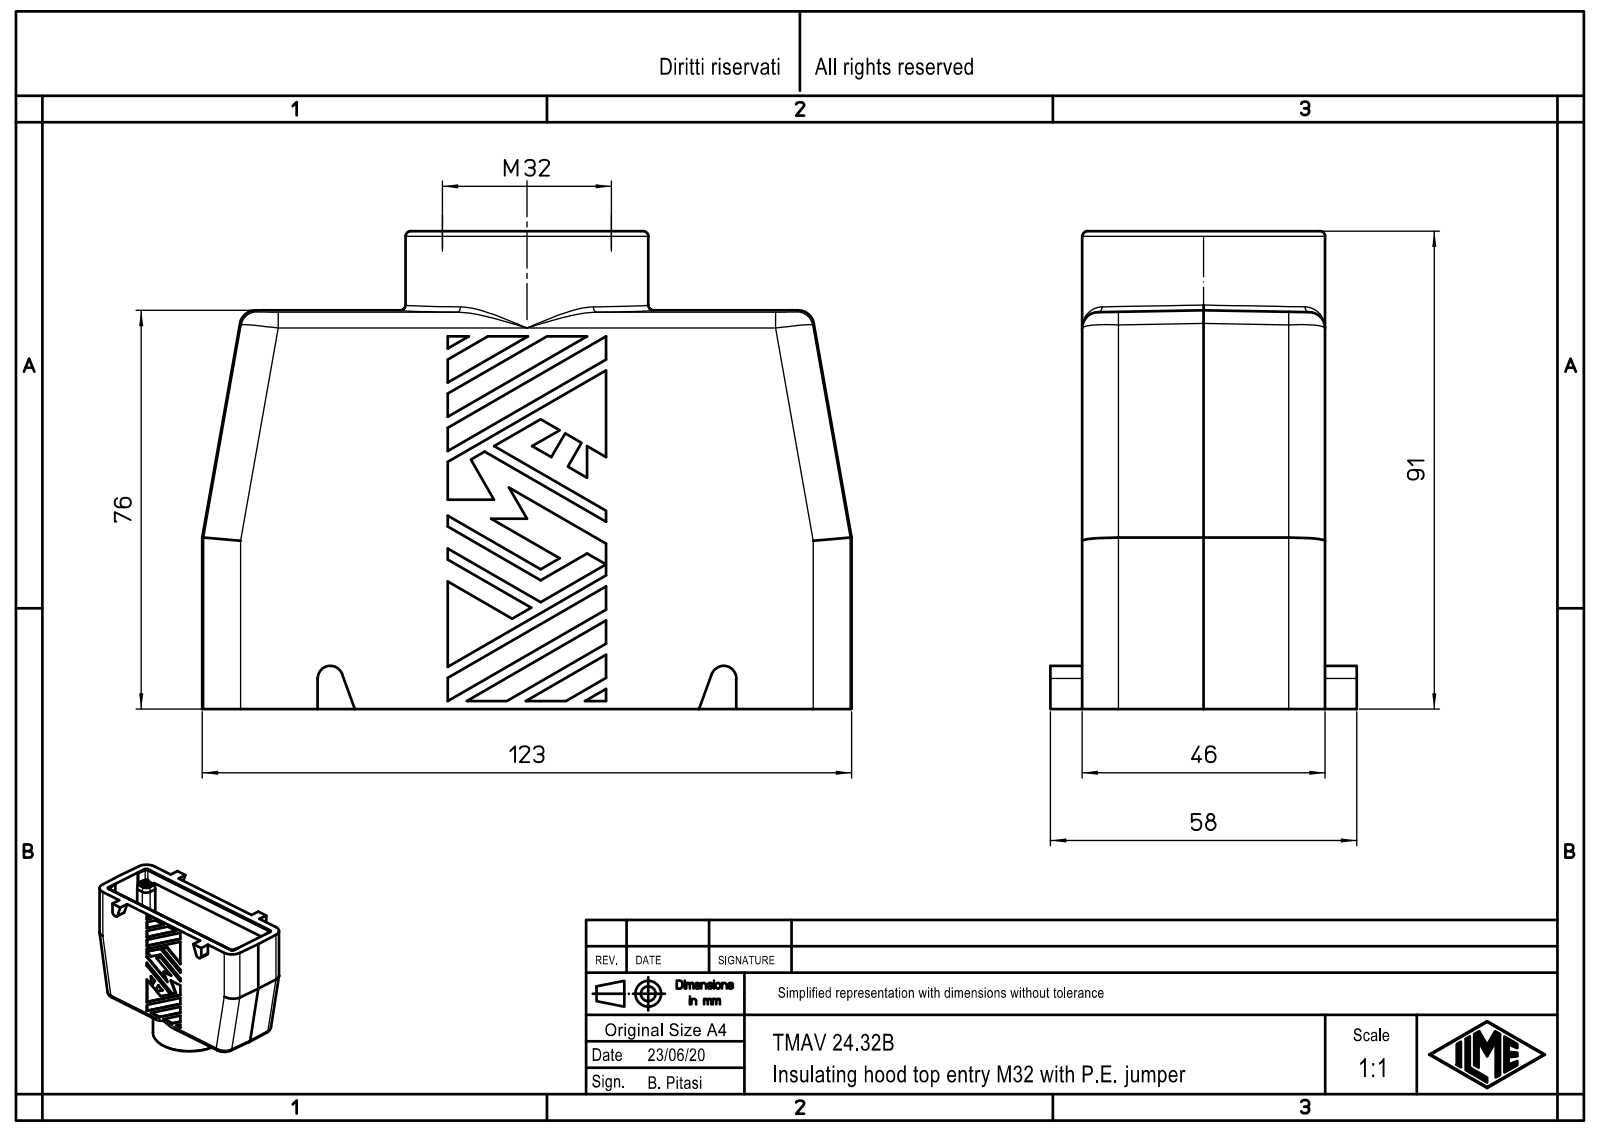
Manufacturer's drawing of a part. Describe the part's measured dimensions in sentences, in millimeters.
The part is named "TMAV_24.32B". Its 3-D file was written by "Creo Elements/Direct Modeling 20.1B 02-Apr-2019 (C) Parametric Technology GmbH (AUTOMOTIVE_DESIGN)". It is 1 solid with 466 faces: 302 planar, 82 cylindrical and 82 other. Overall it measures 123 by 90.49 by 58 millimeters. Its volume is 165 006 cubic millimeters and its surface area 62 339 square millimeters. Round holes: 4 of diameter 3, 4 of diameter 3.5, 1 of diameter 28, 1 of diameter 32. Round bosses or shafts: 4 of diameter 4.8, 1 of diameter 46. Partial cylindrical surfaces (rounded edges, fillets, slot ends): 12 of radius 1.5, 8 of radius 7, 6 of radius 3, 4 of radius 1.3, 4 of radius 1.6, 4 of radius 2, 4 of radius 3.5, 2 of radius 2.4. The main face-to-face distances are 46, 0.5, 45.5, 69.99, 5.6, 40.2, 5.3, 5.8, 39.7, 6.1. The hole center spacings are 53.72, 27, 104, 107.45.
